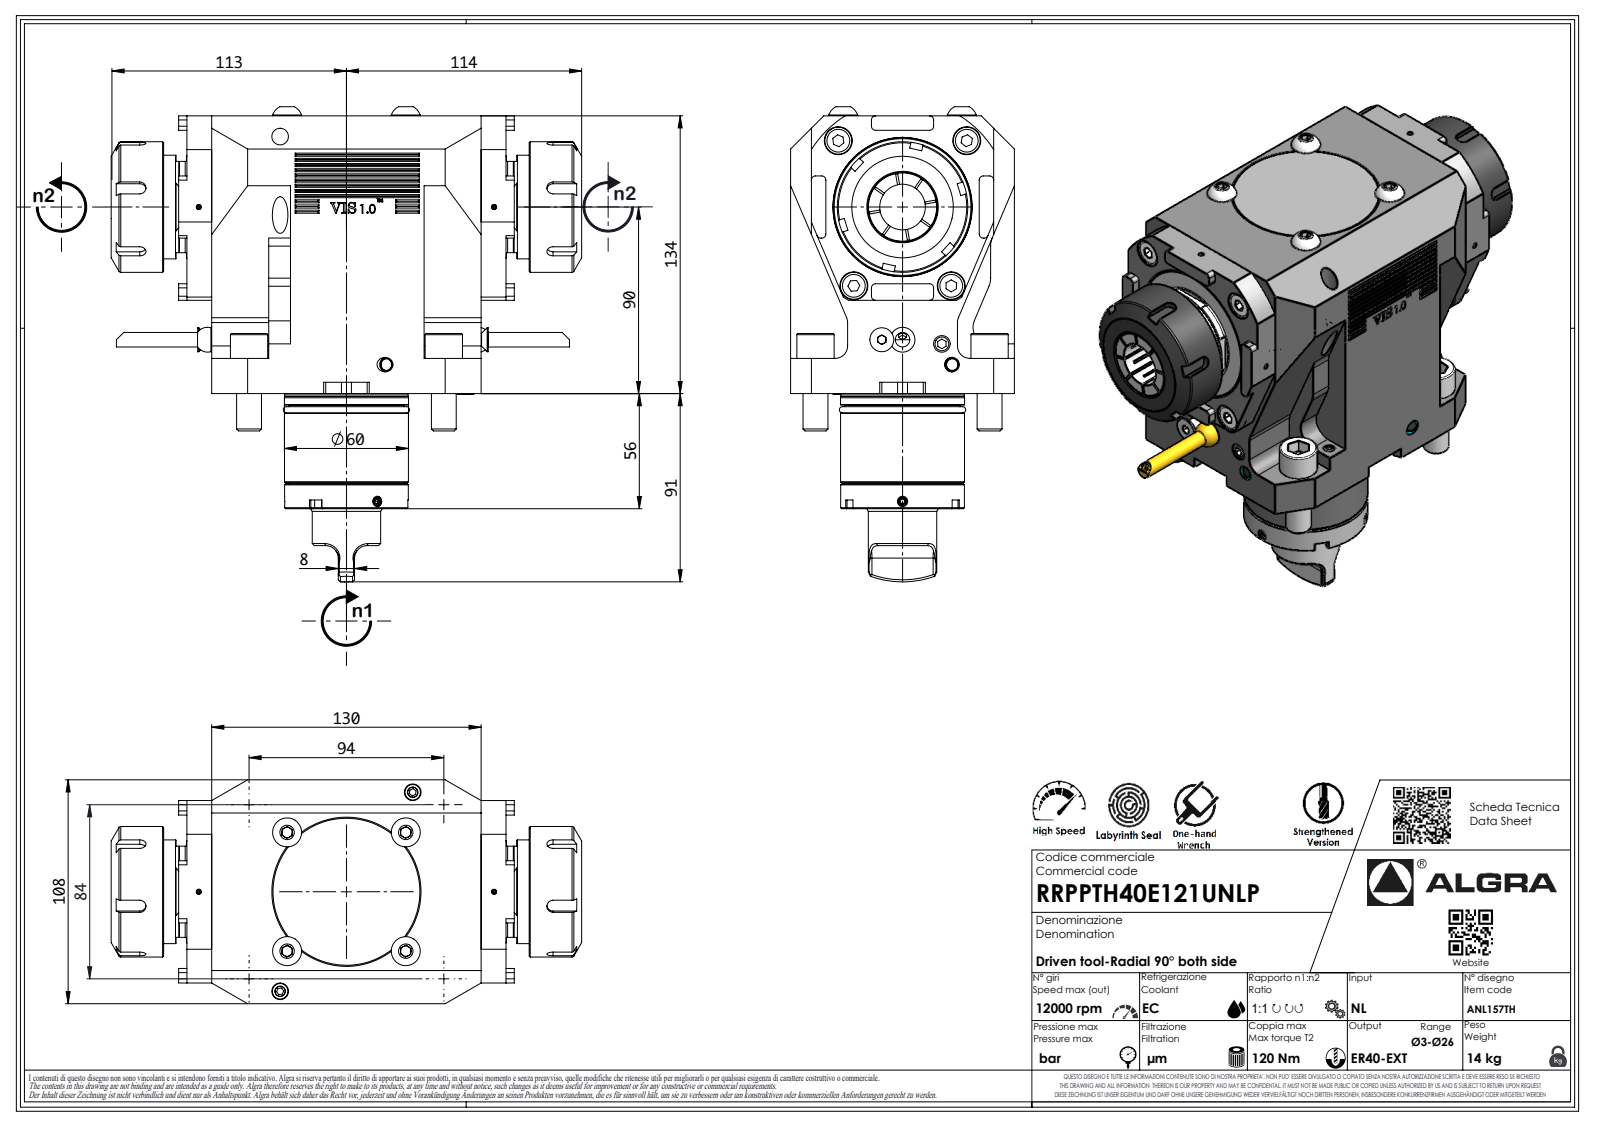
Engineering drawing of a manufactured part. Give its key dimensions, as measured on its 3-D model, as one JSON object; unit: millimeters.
{"part_name": "RRPPTH40E121UNLP", "step_written_by": "SolidWorks 2023 (AUTOMOTIVE_DESIGN)", "units": "millimeters", "bodies": {"solids": 1, "faces": 1114, "planar": 743, "cylindrical": 172, "other": 199}, "overall_size": [227.05, 224.8, 108], "volume_mm3": 2210000, "surface_area_mm2": 145010, "round_holes": [[4, 2], [2.1, 1]], "round_bosses_or_shafts": [[18, 4], [12, 4], [63, 1], [59.9, 1], [59.8, 1], [59.7, 1], [59.5, 1], [55.2, 1]], "partial_cylinders_radius": [[0.2, 21], [8, 18], [2, 16], [3, 15], [6, 10], [0.33, 7], [0.52, 7], [3.7, 7]], "face_to_face_distances": [108, 12, 134, 142, 39.5, 27.5, 154, 114.5, 102.5, 36.53]}
